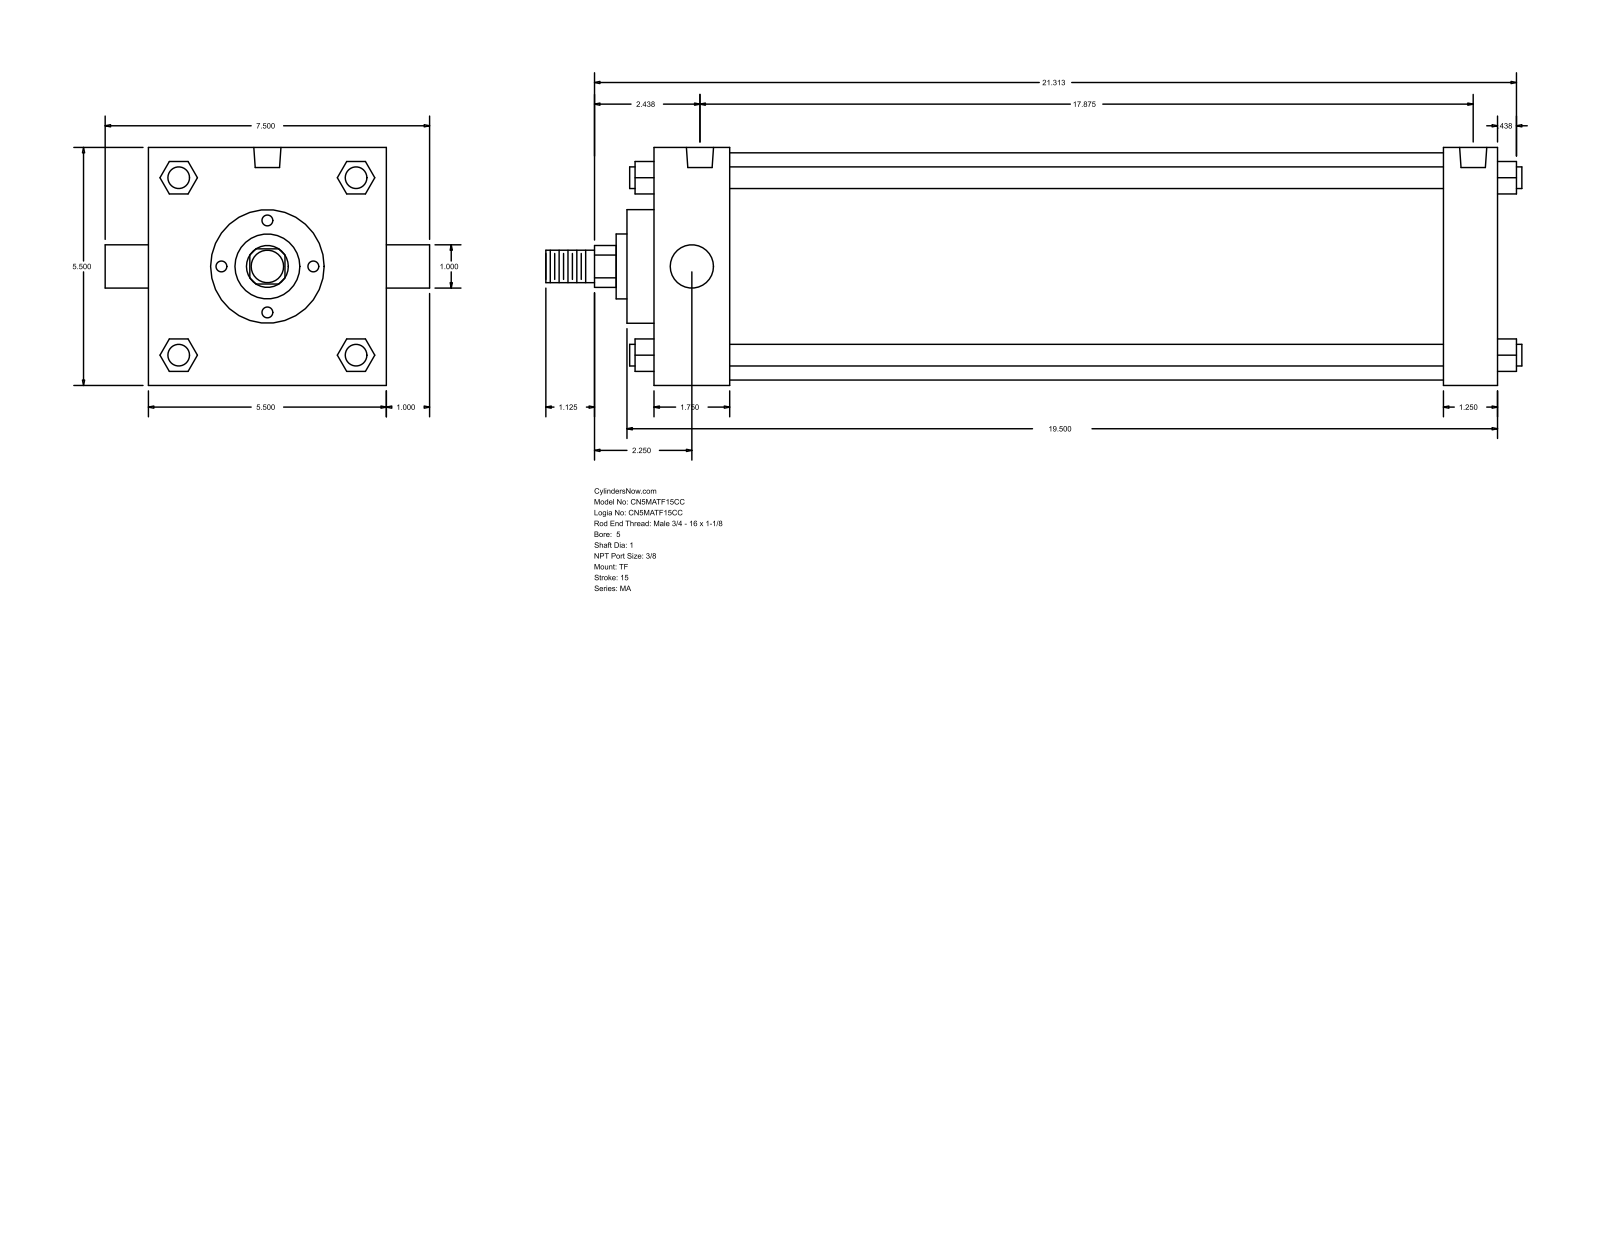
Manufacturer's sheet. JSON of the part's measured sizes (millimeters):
{"part_name": "MA_TF__0500_1", "step_written_by": "GSSL Pune (CONFIG_CONTROL_DESIGN)", "units": "millimeters", "bodies": {"solids": 0, "faces": 122, "planar": 93, "cylindrical": 29, "other": 0}, "overall_size": [573.09, 190.5, 139.7], "round_holes": [[11.11, 3], [15.93, 2]], "round_bosses_or_shafts": [[12.7, 4], [25.4, 2], [133.35, 1], [66.67, 1], [38.1, 1], [19.05, 1]], "partial_cylinders_radius": [[12.29, 1]], "face_to_face_distances": [139.7, 495.31, 463.56, 31.75, 44.46, 419.1, 450.85, 15.87, 60.33, 479.43], "hole_center_spacings": [4.76, 449.27, 444.51, 454.03]}
